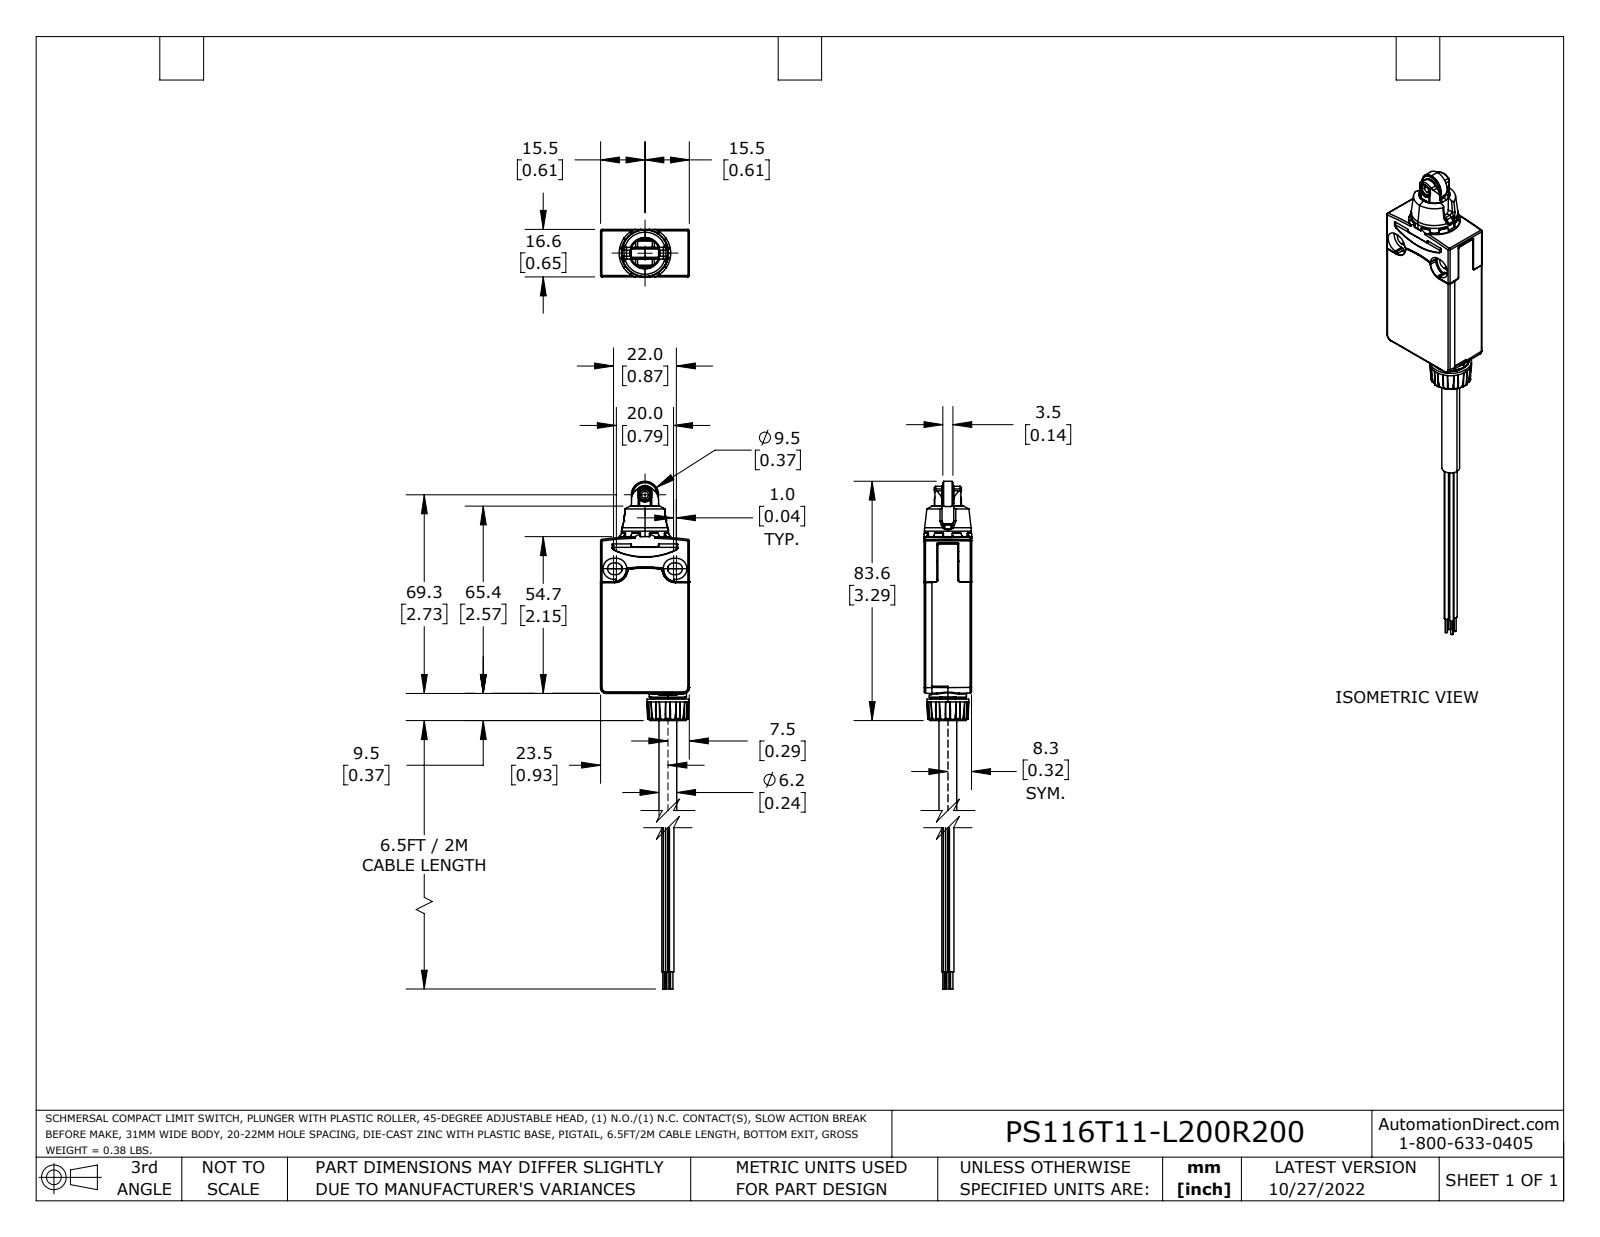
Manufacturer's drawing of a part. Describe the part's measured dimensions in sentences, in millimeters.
The part is named "PS116T11-L200R200_Default". Its 3-D file was written by "SolidWorks 2021 (CONFIG_CONTROL_DESIGN)". It is 2 solids with 1214 faces: 350 planar, 504 cylindrical and 360 other. Overall it measures 191.5 by 31 by 16.6 millimeters. Its volume is 30 400 cubic millimeters and its surface area 14 630 square millimeters. Round holes: 1 of diameter 2, 1 of diameter 2.4, 1 of diameter 3.1, 1 of diameter 3.5, 1 of diameter 5, 1 of diameter 6.4, 1 of diameter 6.7, 1 of diameter 11.6, 1 of diameter 12.2, 1 of diameter 14.5. Round bosses or shafts: 4 of diameter 1.5, 4 of diameter 0.8, 2 of diameter 13, 1 of diameter 16.4, 1 of diameter 14.5, 1 of diameter 14.4, 1 of diameter 13.3, 1 of diameter 11.4. Partial cylindrical surfaces (rounded edges, fillets, slot ends): 144 of radius 0.2, 73 of radius 0.1, 38 of radius 0.5, 22 of radius 1, 10 of radius 0.4, 6 of radius 0.3, 5 of radius 2, 4 of radius 2.1. The main face-to-face distances are 16.5, 16.6, 31, 1.7, 3, 2.9, 16.6, 3.5, 5.6, 1. The hole center spacings are 8.
